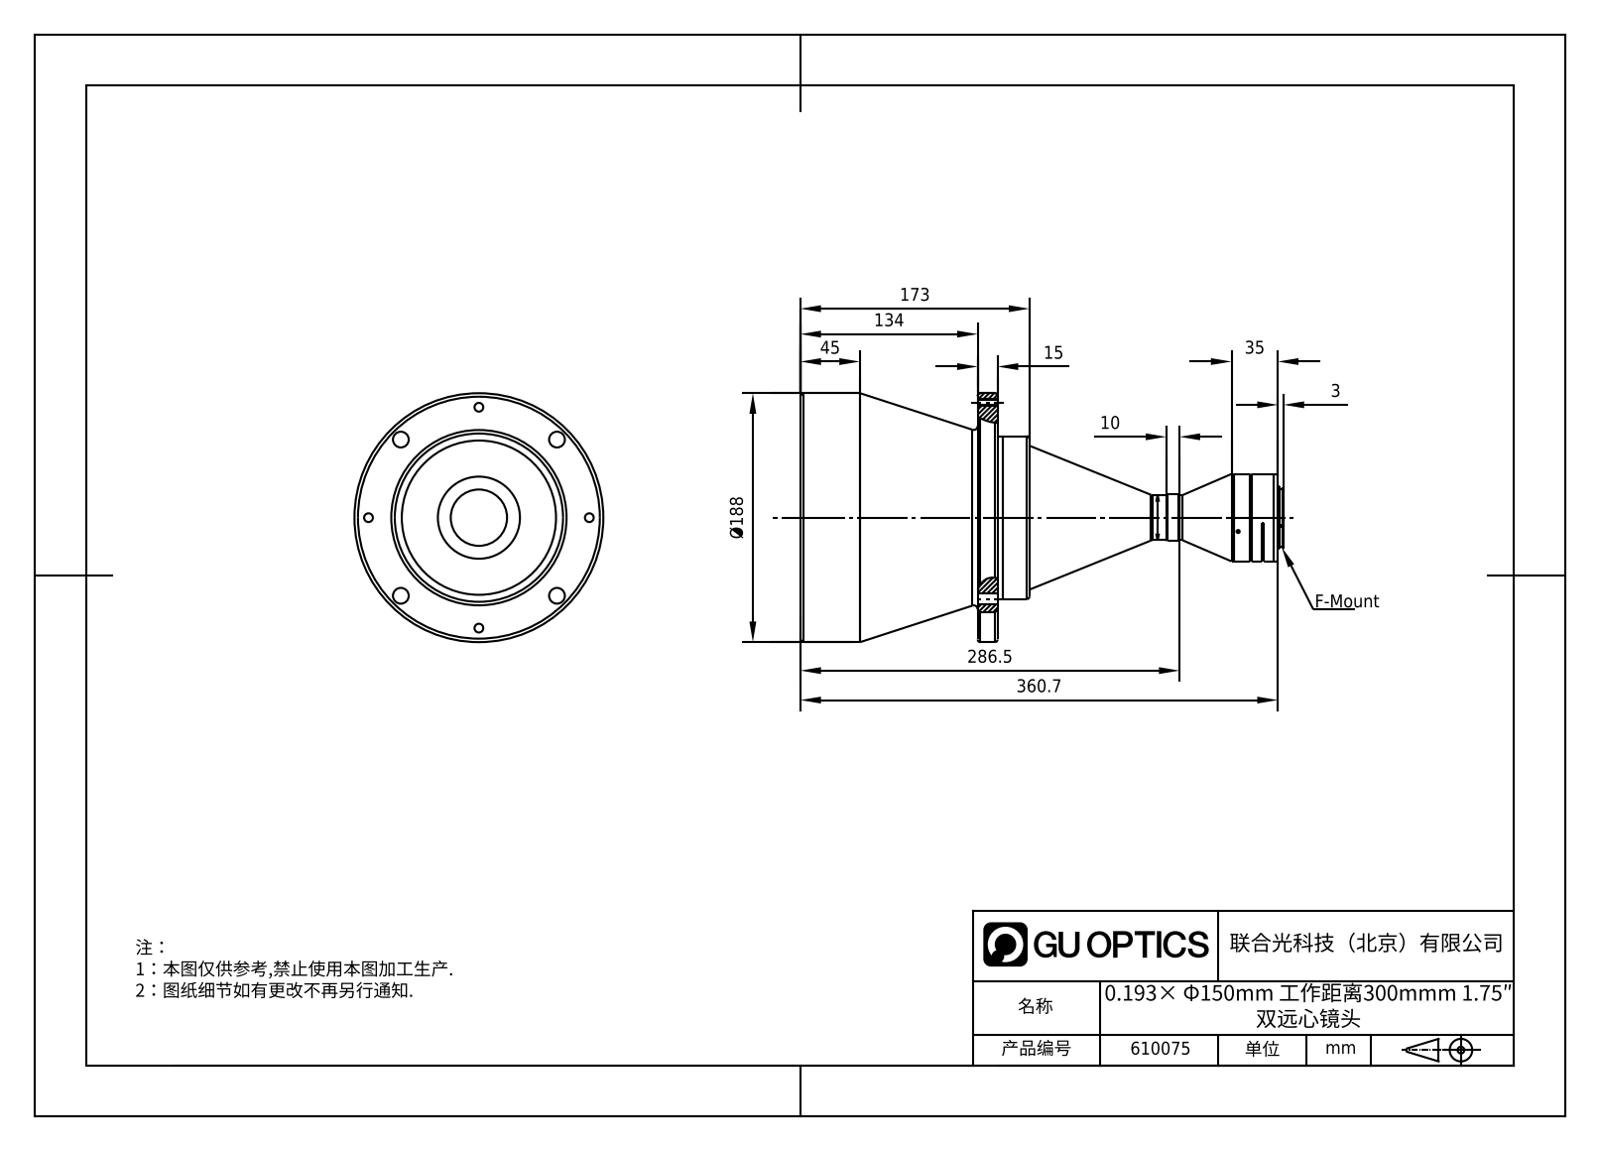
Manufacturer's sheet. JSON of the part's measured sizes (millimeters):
{"part_name": "DTCM175-150-AL", "step_written_by": "SolidWorks 2017 (CONFIG_CONTROL_DESIGN)", "units": "millimeters", "bodies": {"solids": 1, "faces": 62, "planar": 8, "cylindrical": 32, "other": 22}, "overall_size": [363.7, 188, 188], "volume_mm3": 4272000, "surface_area_mm2": 193598, "round_holes": [[5, 4], [8, 4]], "round_bosses_or_shafts": [[188, 1], [123, 1], [66, 1], [44, 1], [35, 1], [34, 1]], "face_to_face_distances": [149, 134, 15, 360.7, 226.7, 211.7, 363.7, 229.7, 214.7, 3], "hole_center_spacings": [66.59, 123.04, 160.76, 174]}
